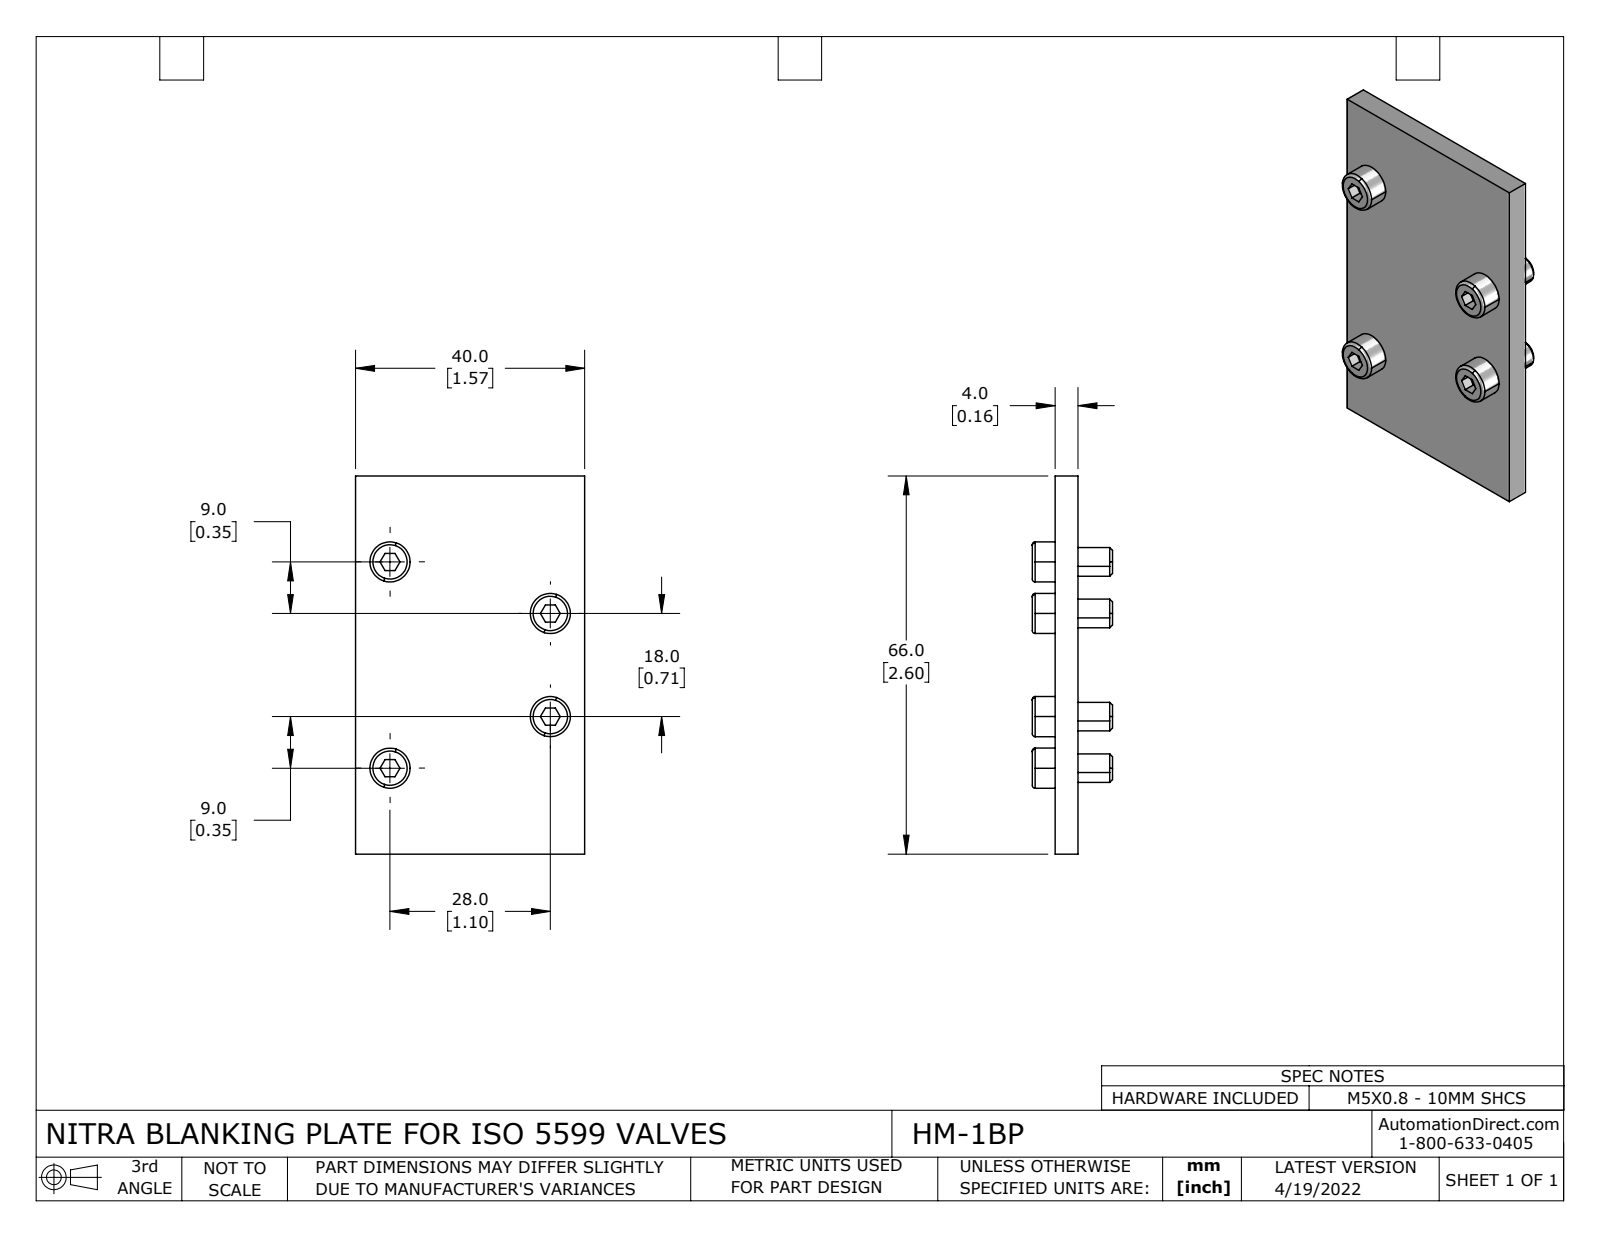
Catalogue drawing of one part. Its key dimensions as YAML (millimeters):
part_name: "HM-1BP"
step_written_by: "SolidWorks 2021 (CONFIG_CONTROL_DESIGN)"
units: millimeters
bodies: {solids: 1, faces: 86, planar: 46, cylindrical: 24, other: 16}
overall_size: [66, 40, 14]
volume: 11507
surface_area: 7429
round_holes:
  - {diameter: 5.5, count: 4}
round_bosses_or_shafts:
  - {diameter: 7, count: 4}
  - {diameter: 5, count: 4}
face_to_face_distances: [4, 40, 66, 6, 8, 2, 10, 14, 12, 3]
hole_center_spacings: [29.41, 38.9, 18, 36]
